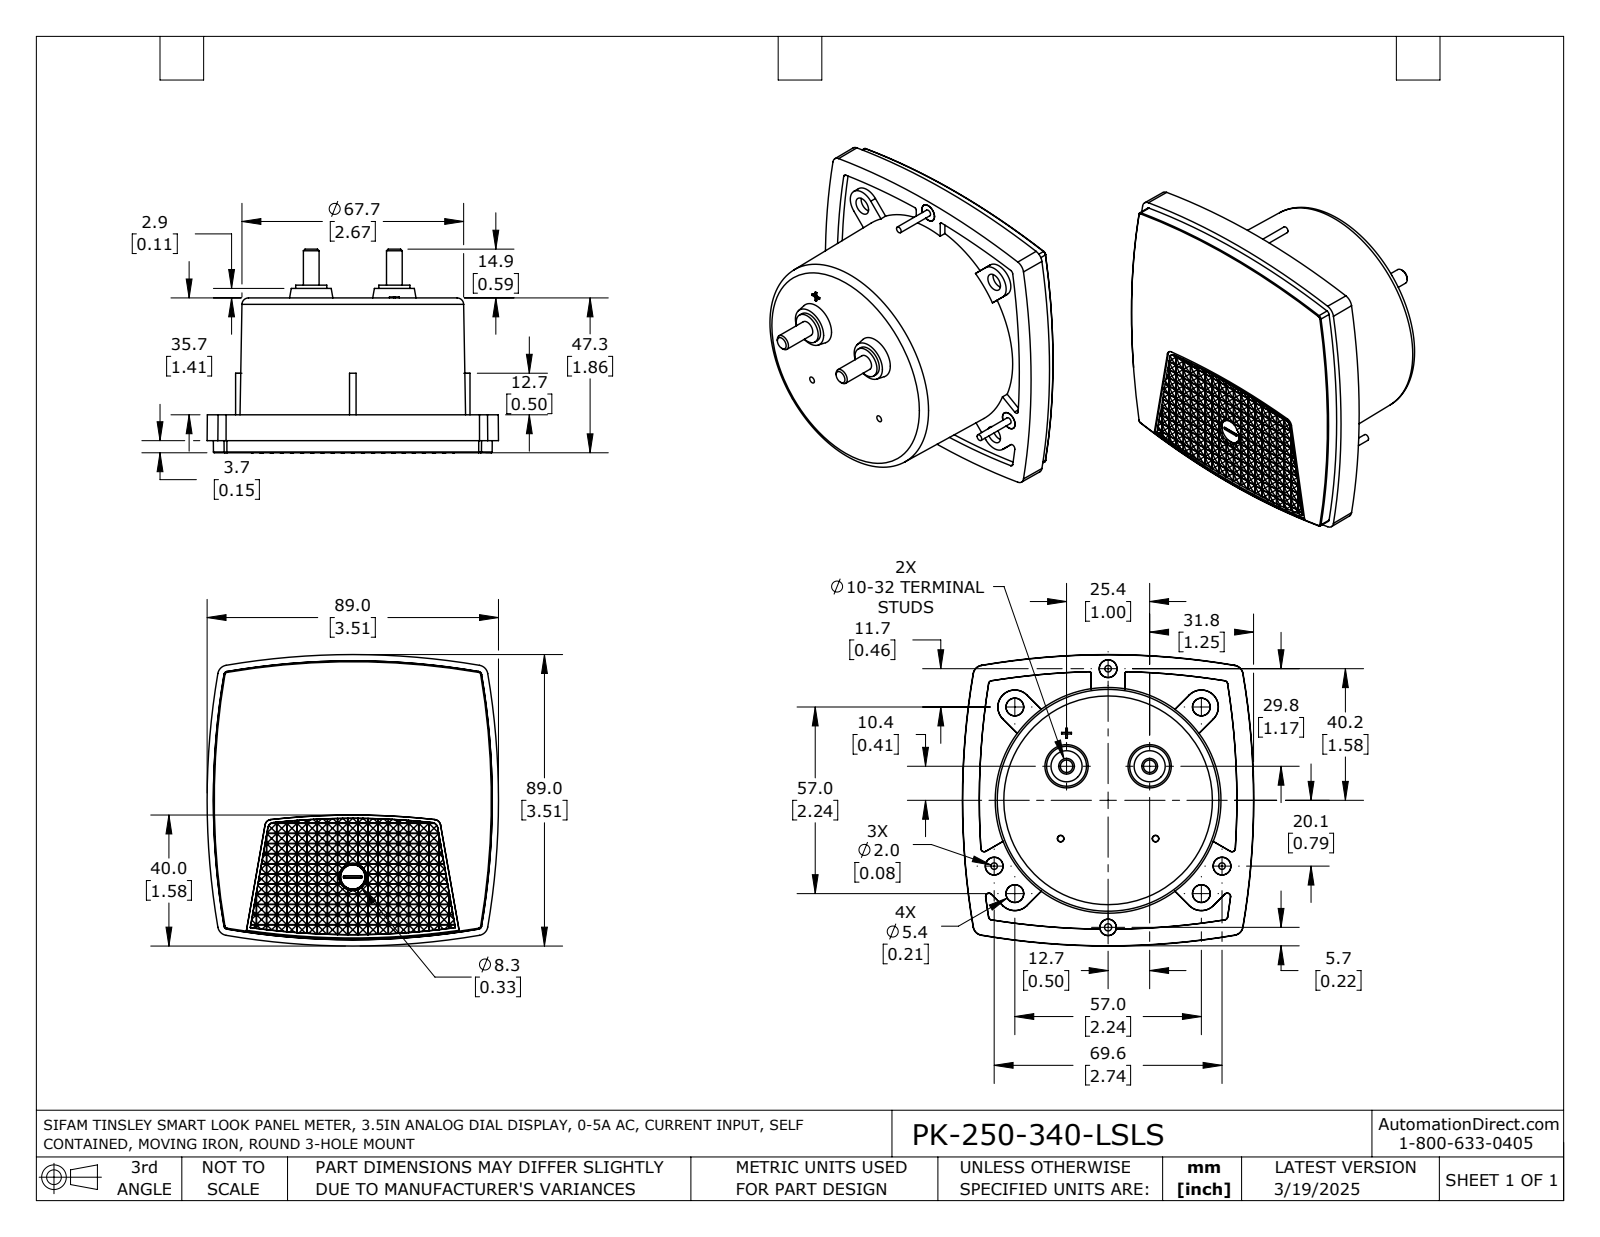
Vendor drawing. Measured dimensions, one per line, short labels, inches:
name: PK-250-340-LSLS
written by: SolidWorks 2021 (AUTOMOTIVE_DESIGN)
unit: in
bodies: 1 solid, 1078 faces (950 planar, 23 cylindrical, 105 other)
size: 3.505 × 3.505 × 2.453
volume: 12.99 in³; area: 44.29 in²
holes: 1× ⌀0.087
bosses: 3× ⌀0.213, 3× ⌀0.079, 2× ⌀0.374, 2× ⌀0.189
rounds: 1× R8.961
face distances: 1.862, 1.406, 0.457, 0.079, 1.484, 0.378, 0.024, 0.096, 0.072, 0.12
